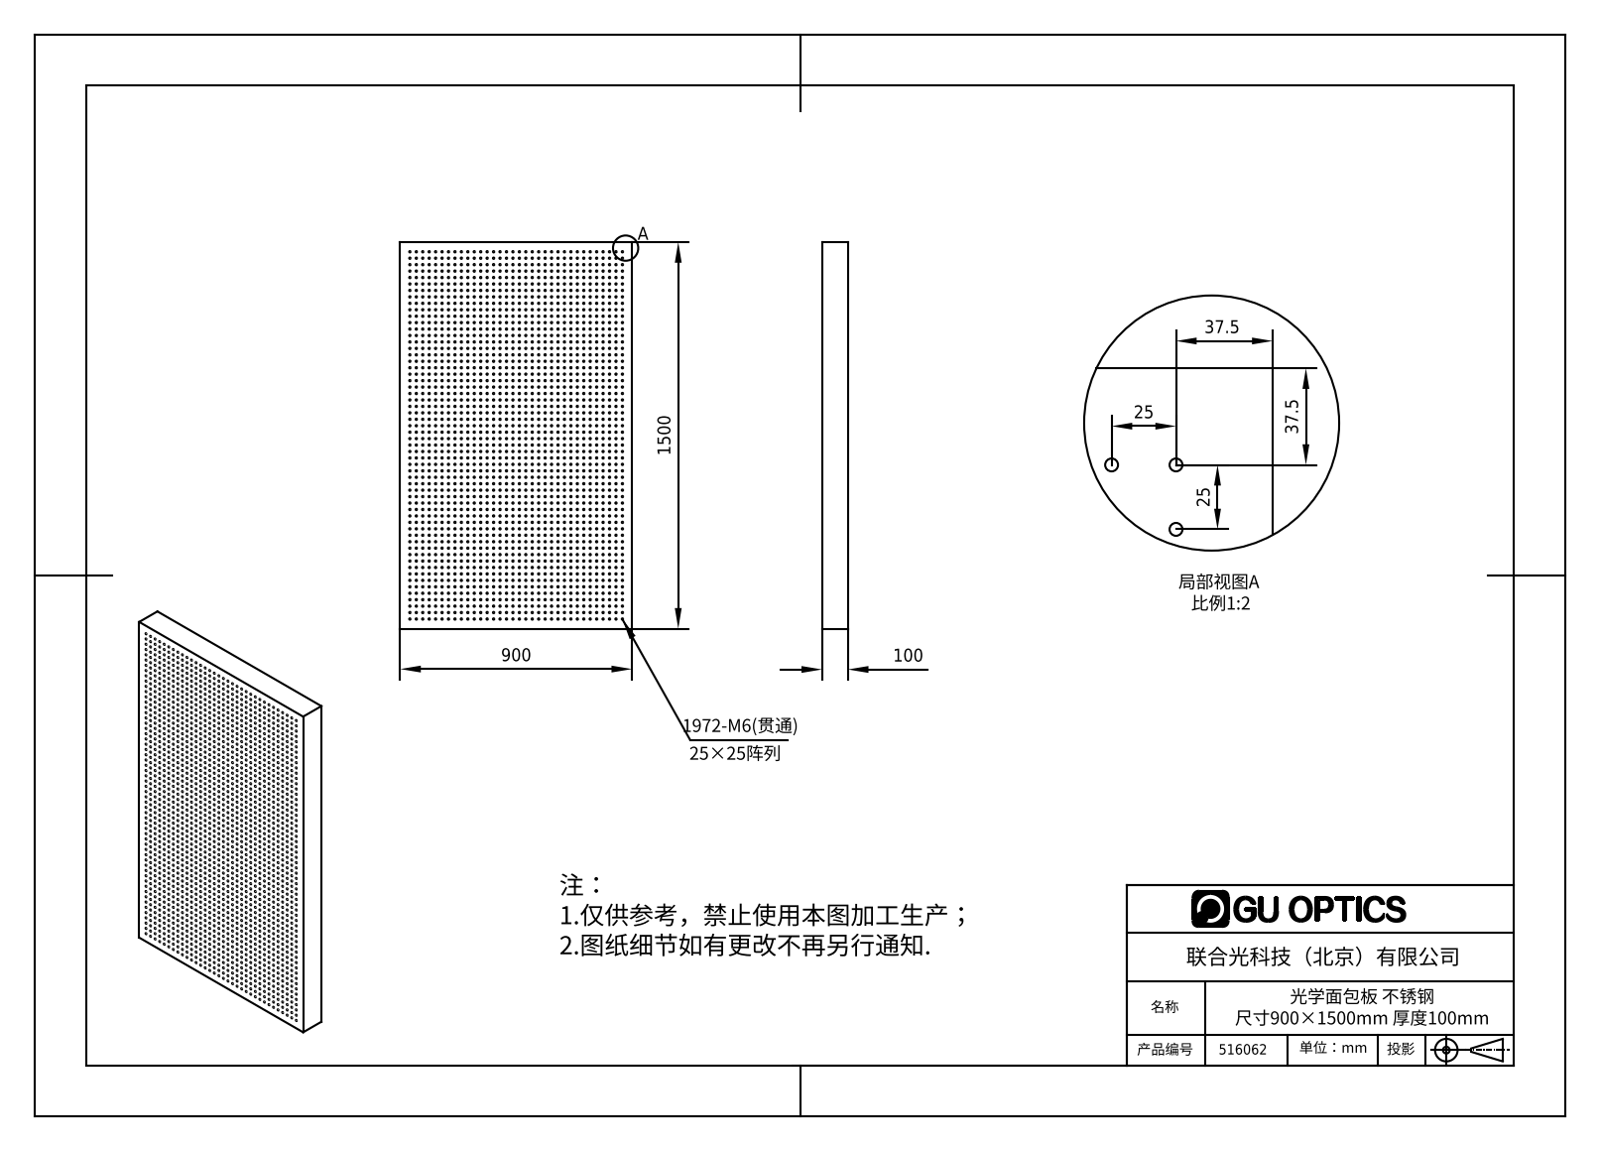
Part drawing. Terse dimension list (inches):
name: 516062
written by: SolidWorks 2020 (CONFIG_CONTROL_DESIGN)
unit: in
bodies: 1 solid, 5976 faces (2016 planar, 3960 cylindrical, 0 other)
size: 59.055 × 35.433 × 3.937
volume: 7 890 in³; area: 5 439 in²
holes: 1972× ⌀0.209
rounds: 4× R0.079, 4× R0.118, 4× R0.433
face distances: 3.937, 34.409, 0.236, 3.701, 58.031, 3.74, 3.504, 0.197, 0.512, 34.921
hole spacings: 3.113, 1.392, 1.969, 5.019, 2.784, 6.96, 3.937, 4.402
